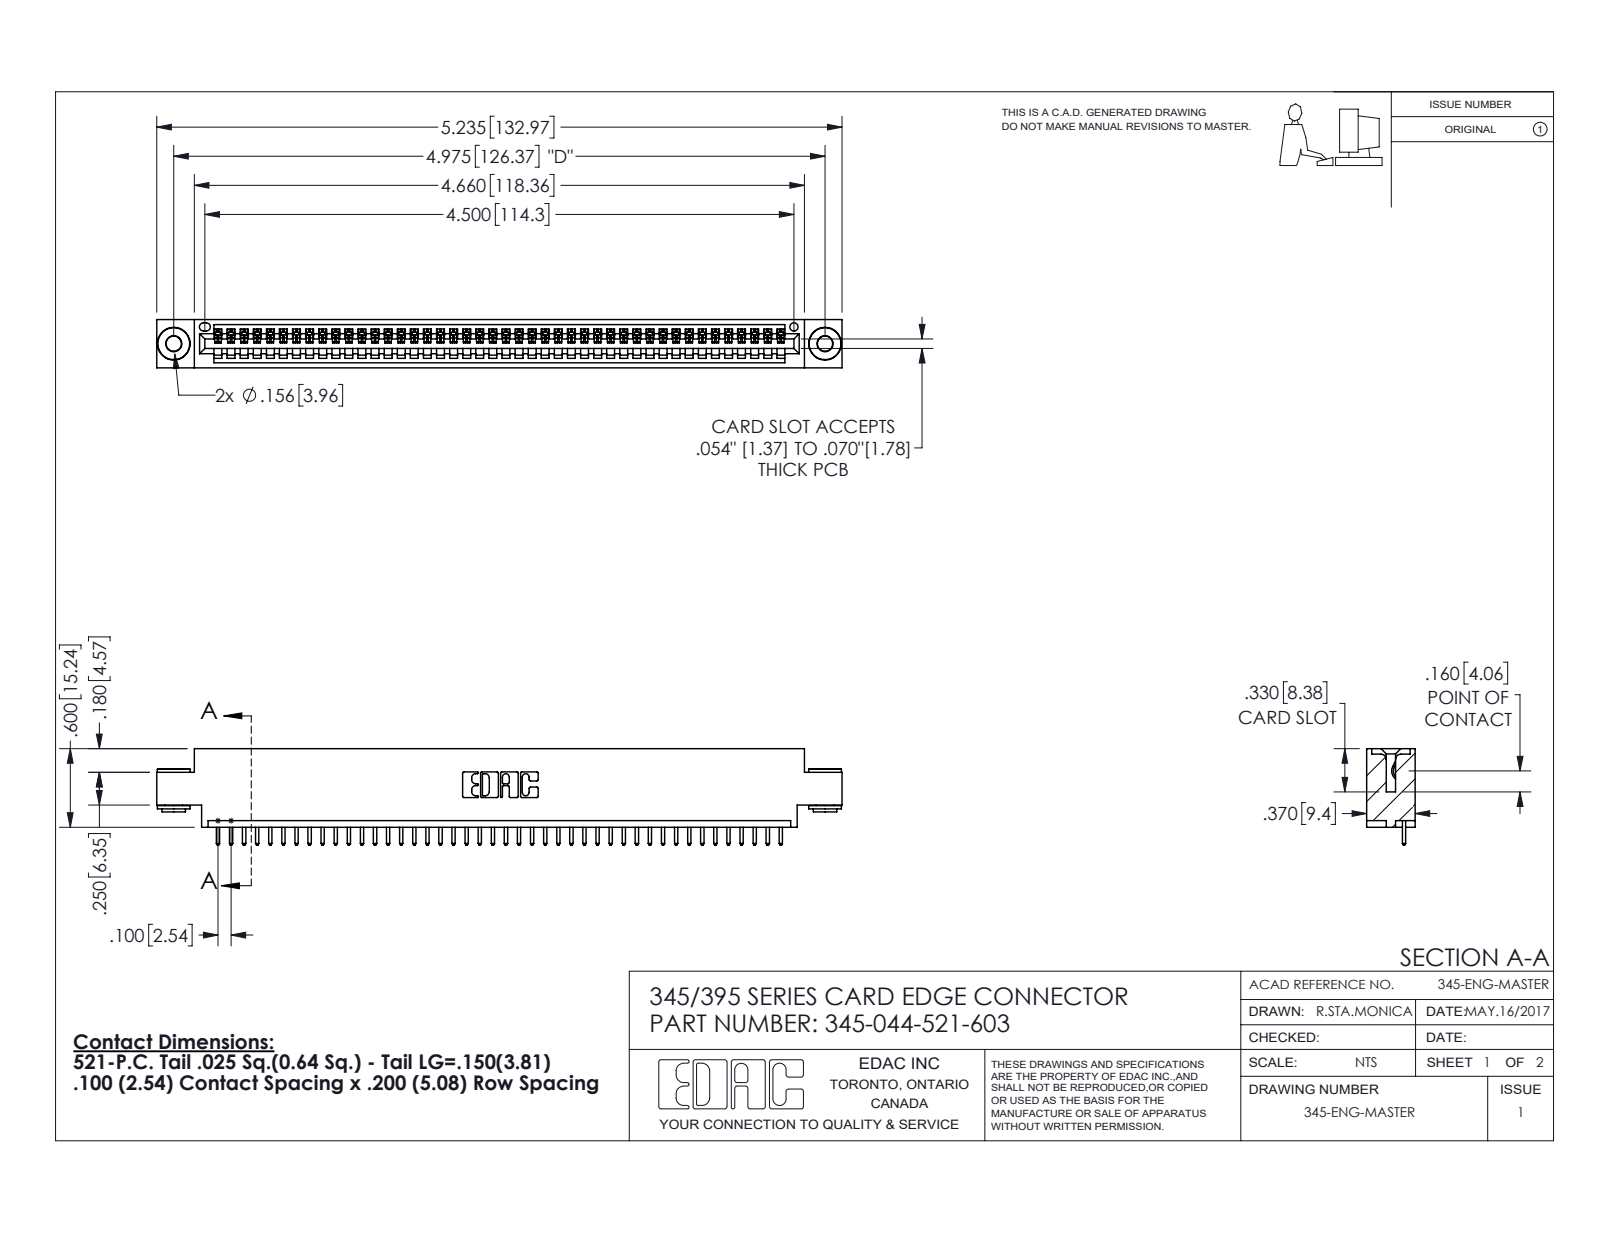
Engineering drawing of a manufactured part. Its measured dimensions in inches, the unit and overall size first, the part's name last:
Units: inches
Overall size (bounding box): 5.235 × 0.737 × 0.37
Round holes (diameter × count): ⌀0.116 ×2, ⌀0.156 ×2, ⌀0.064 ×1
Round bosses / shafts (diameter × count): ⌀0.25 ×2, ⌀0.18 ×2, ⌀0.136 ×2
Partial cylindrical surfaces — rounded edges, fillets, slot ends (radius × count): R0.006 ×88, R0.01 ×88, R0.01 ×22, R0.007 ×6, R0.031 ×6, R0.026 ×3, R0.031 ×2, R0.04 ×2
Main face-to-face distances: 0.072, 0.298, 0.37, 0.2, 0.098, 0.272, 0.025, 0.225, 0.175, 0.149
Hole centre spacings: 0.27, 4.739, 4.975
Volume: 0.758 in³ · Surface area: 25.41 in²
Bodies: 47 solids, 2720 faces (1854 planar, 858 cylindrical, 8 other)
Part name (STEP PRODUCT): 345-044-521-603; 345-292-001_345-293-121; 345-250-002_345-250-002-102; 345 Part_0.170 Offset - 0.156 Dia-TH
STEP written by: SolidWorks 2016 (CONFIG_CONTROL_DESIGN)
